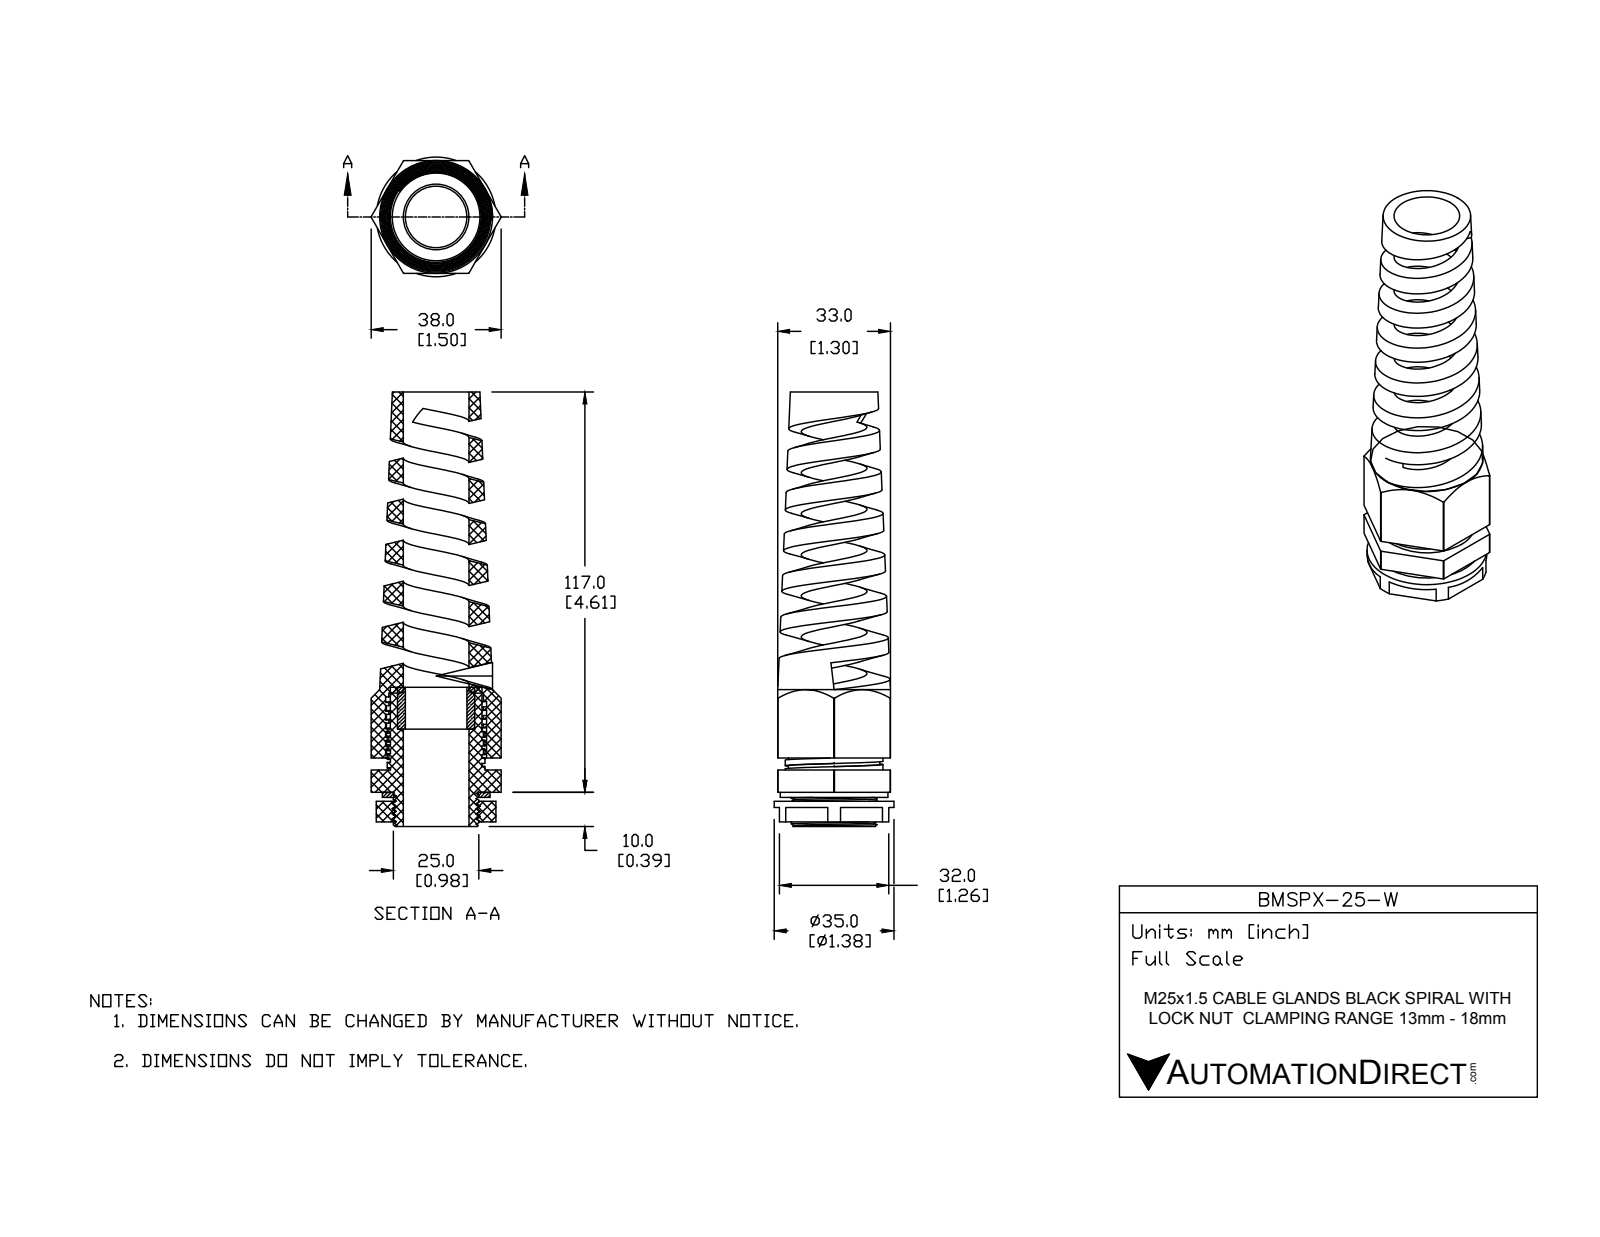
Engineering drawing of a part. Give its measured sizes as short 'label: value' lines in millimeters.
name: BMSPX-25-W
written by: SolidWorks 2015 (CONFIG_CONTROL_DESIGN)
unit: mm
bodies: 5 solids, 235 faces (103 planar, 93 cylindrical, 39 other)
size: 127 × 38 × 35
volume: 41 219 mm³; area: 32 760 mm²
holes: 1× ⌀18, 1× ⌀19.2, 1× ⌀22.6, 1× ⌀24.19, 1× ⌀24.7, 1× ⌀27.67
bosses: 1× ⌀35, 1× ⌀31.5, 1× ⌀28.6, 1× ⌀26.8, 1× ⌀25
rounds: 1× R19
face distances: 33, 0.5, 8.5, 2.5, 1.5, 10, 6, 32.5, 15, 18.5
